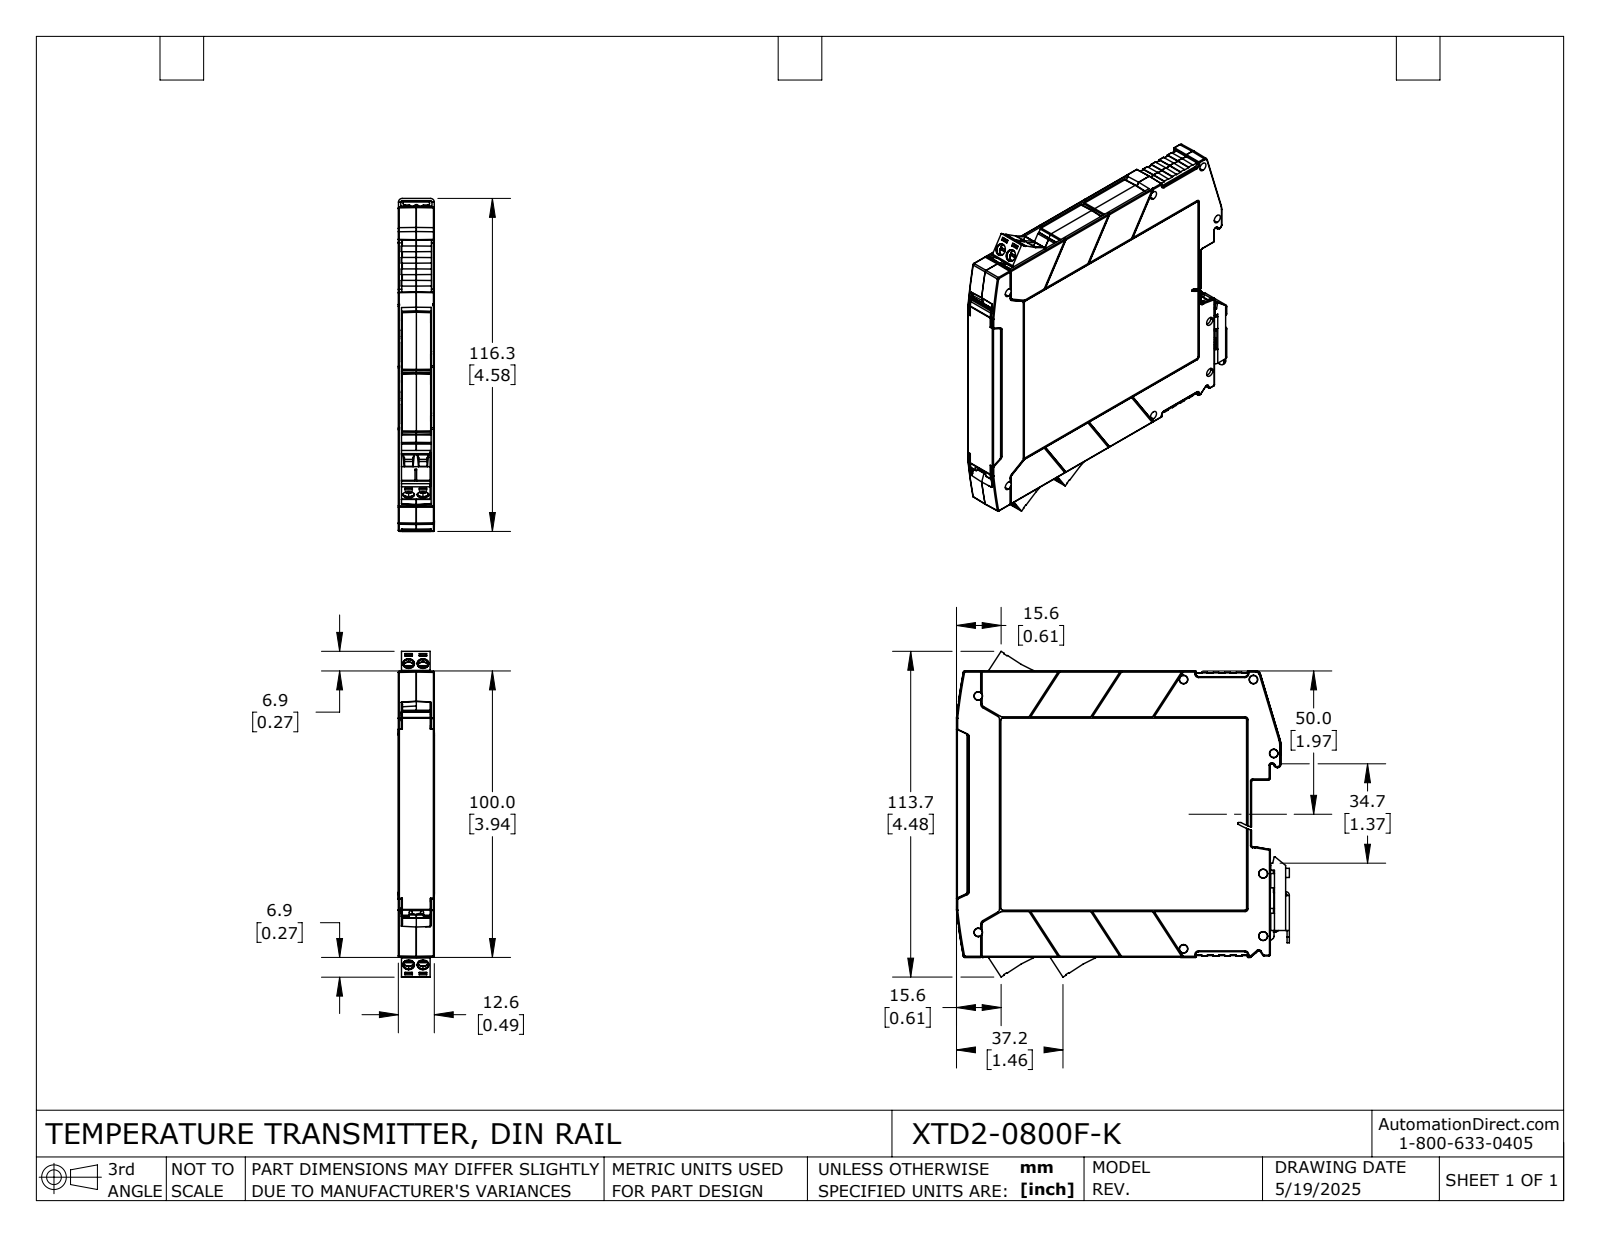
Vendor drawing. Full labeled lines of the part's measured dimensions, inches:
Part name (STEP PRODUCT): XTD2-0800F-K
STEP written by: SolidWorks 2024 (AUTOMOTIVE_DESIGN)
Units: inches
Bodies: 14 solids, 3337 faces (1910 planar, 596 cylindrical, 831 other)
Overall size (bounding box): 4.577 × 4.478 × 0.496
Volume: 2.41 in³ · Surface area: 101.5 in²
Round holes (diameter × count): ⌀0.063 ×6, ⌀0.11 ×6, ⌀0.152 ×6, ⌀0.159 ×6
Round bosses / shafts (diameter × count): ⌀0.156 ×6, ⌀0.098 ×6, ⌀0.059 ×2, ⌀0.053 ×2
Partial cylindrical surfaces — rounded edges, fillets, slot ends (radius × count): R0.008 ×89, R0.012 ×78, R0.02 ×71, R0.039 ×22, R0.004 ×20, R0.016 ×13, R0.006 ×12, R0.028 ×8
Main face-to-face distances: 0.049, 0.445, 0.494, 0.396, 0.043, 0.451, 0.402, 0.031, 0.198, 0.247
Hole centre spacings: 0.197, 0.464, 0.504, 0.713, 0.739
